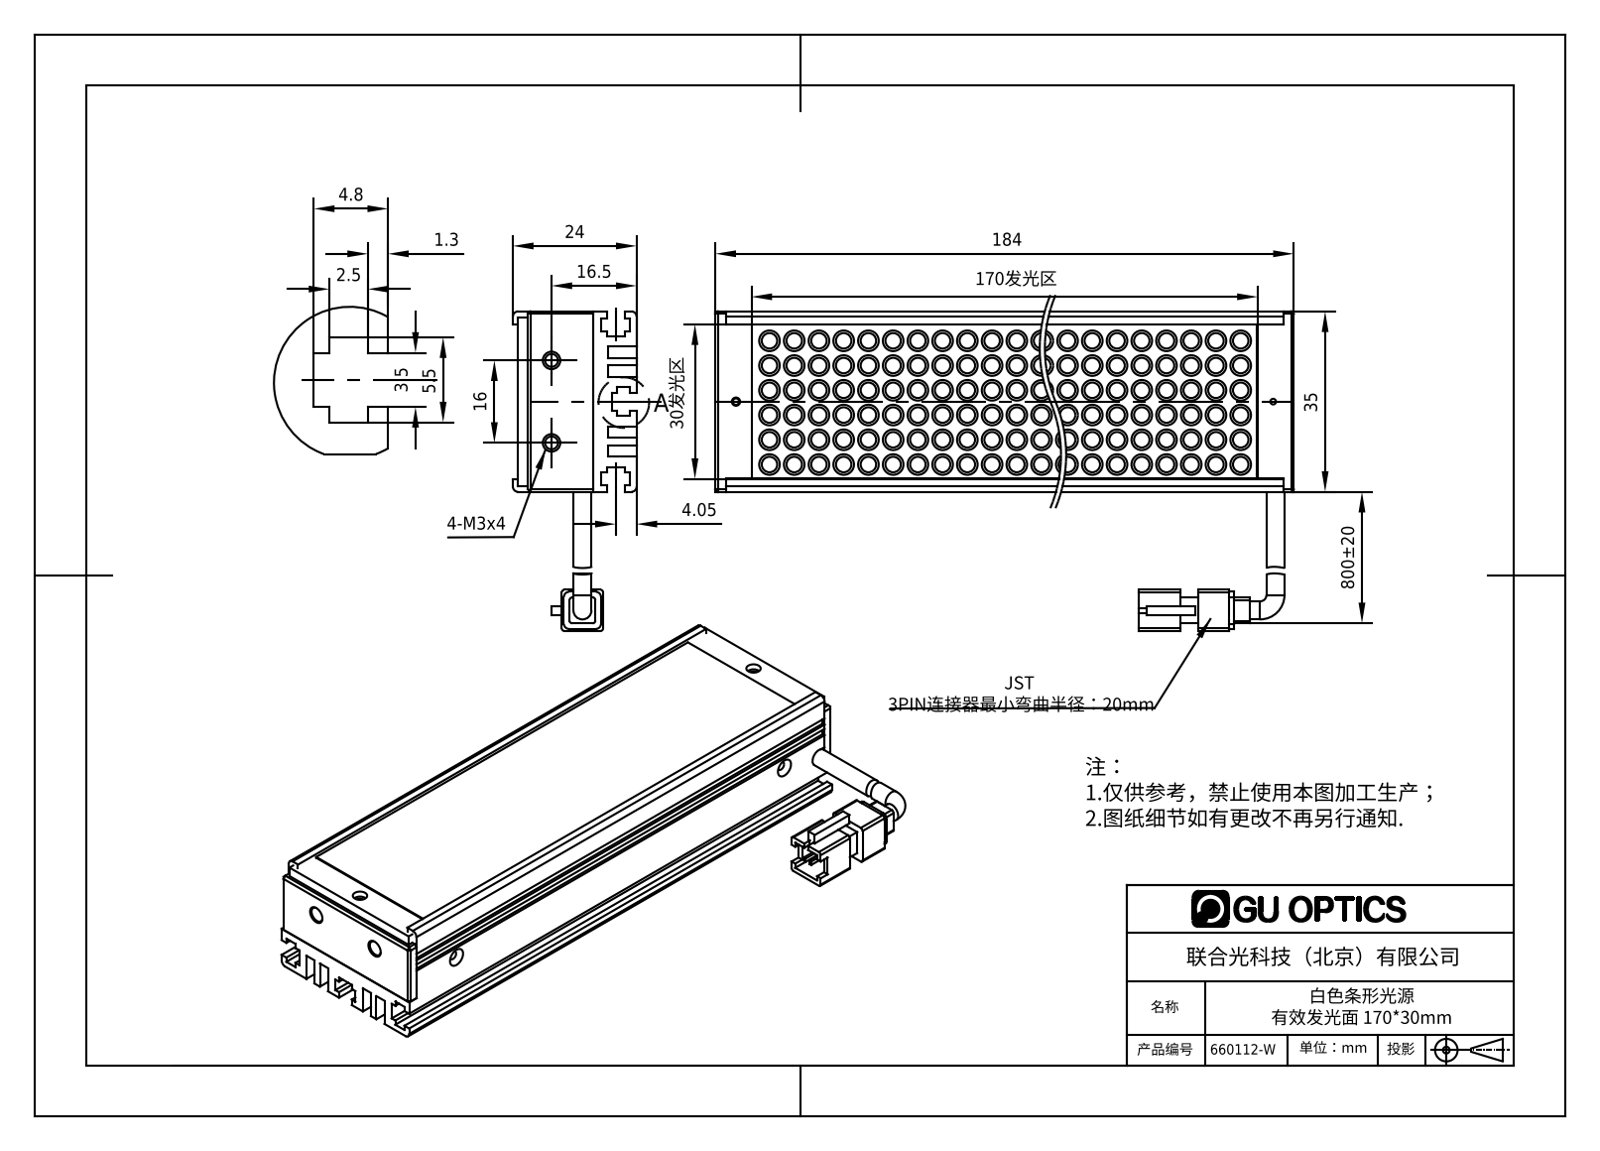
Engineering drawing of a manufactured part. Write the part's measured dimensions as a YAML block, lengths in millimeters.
part_name: "660112-W"
step_written_by: "SolidWorks 2016 (AUTOMOTIVE_DESIGN)"
units: millimeters
bodies: {solids: 8, faces: 1721, planar: 477, cylindrical: 927, other: 317}
overall_size: [184, 62, 24]
volume: 82743
surface_area: 93944
round_holes:
  - {diameter: 1.6, count: 5}
  - {diameter: 1.7, count: 3}
  - {diameter: 1.5, count: 2}
  - {diameter: 2.5, count: 2}
  - {diameter: 2.8, count: 2}
  - {diameter: 3, count: 2}
  - {diameter: 1.1, count: 1}
  - {diameter: 1.25, count: 1}
  - {diameter: 2, count: 1}
round_bosses_or_shafts:
  - {diameter: 4, count: 210}
  - {diameter: 3, count: 210}
  - {diameter: 3.5, count: 2}
partial_cylinders:
  - {radius: 1, count: 12}
  - {radius: 0.5, count: 8}
  - {radius: 1.65, count: 1}
face_to_face_distances: [2, 2.2, 8.6, 1, 2.5, 12.6, 14.6, 9, 4, 10.6]
hole_center_spacings: [176, 7, 28.05, 28.52, 60, 88.01, 88.17, 148.01]
